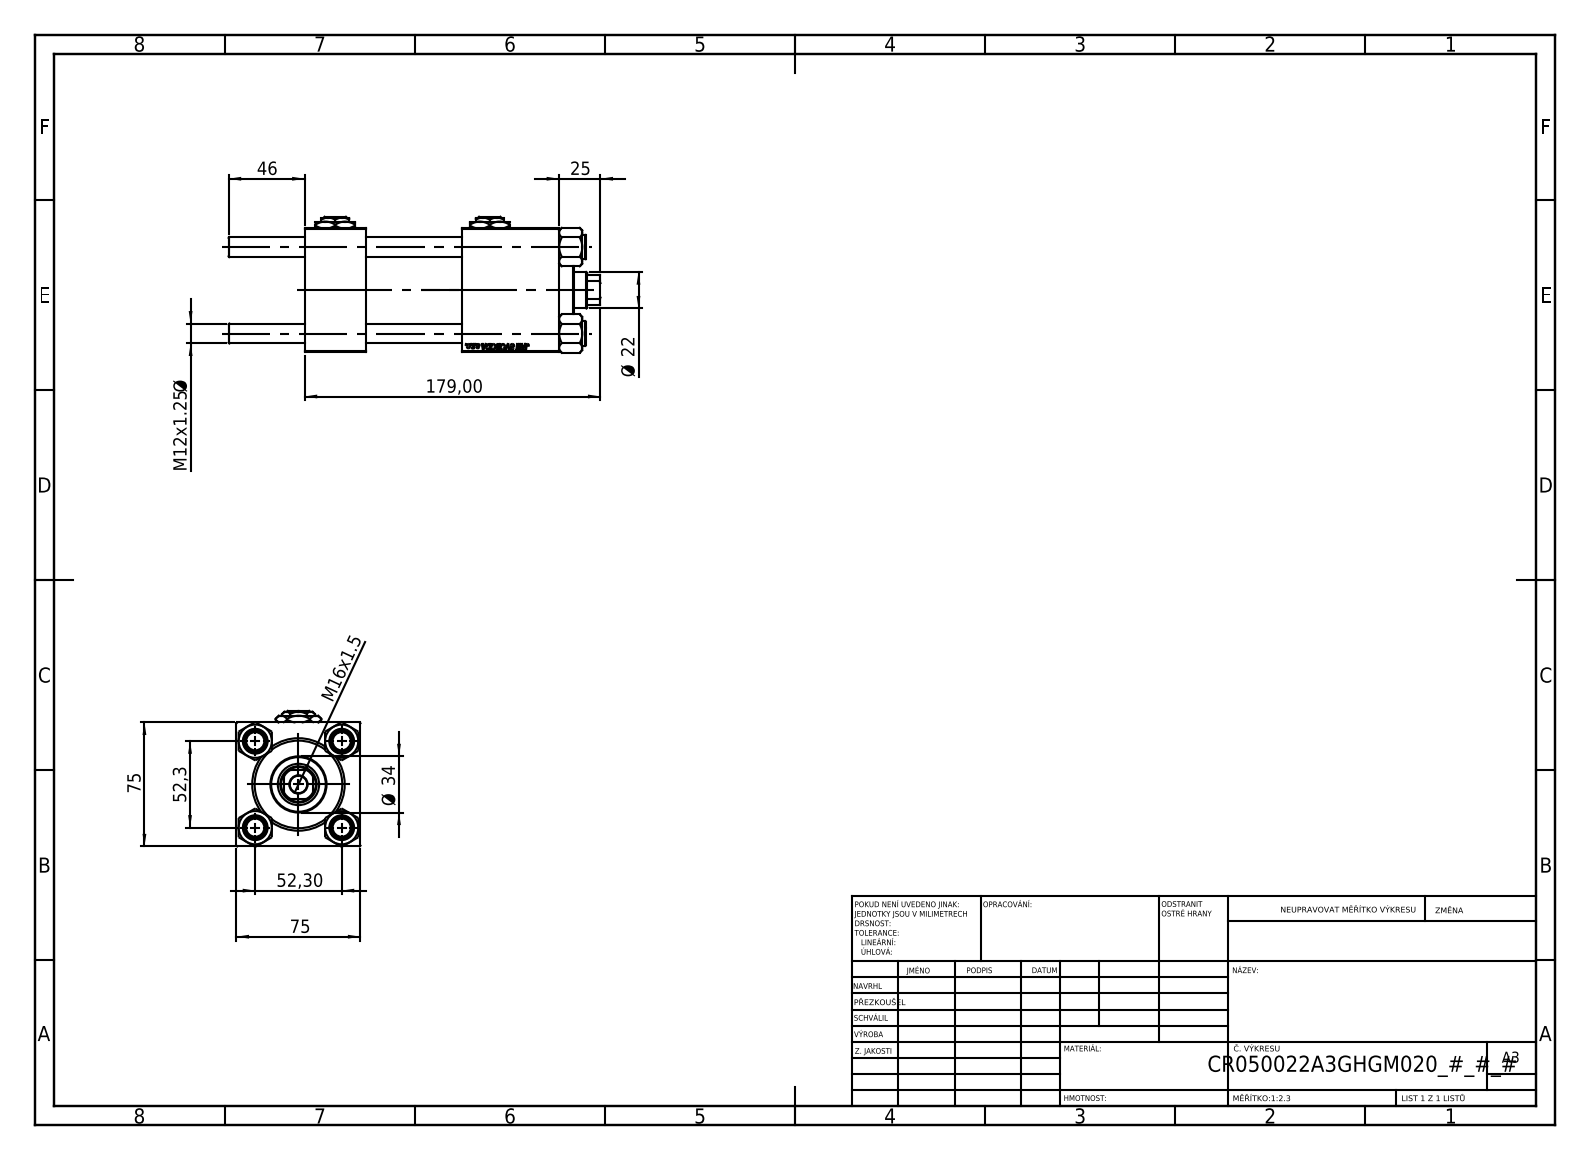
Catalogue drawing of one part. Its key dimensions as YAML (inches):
part_name: "Zatka_pro_OIL_PORT; V215CR_VCP; CR025_012_A_0_G_A_G_M_020_+#_##_TYCINKA; V215CR_BODY_A (+2 more)"
step_written_by: "SolidWorks 2019 (CONFIG_CONTROL_DESIGN)"
units: inches
bodies: {solids: 13, faces: 1233, planar: 567, cylindrical: 88, other: 578}
overall_size: [8.858, 3.239, 2.953]
volume: 41.8
surface_area: 260.7
round_holes:
  - {diameter: 0.472, count: 4}
  - {diameter: 0.276, count: 2}
  - {diameter: 0.825, count: 2}
  - {diameter: 1.181, count: 2}
  - {diameter: 0.413, count: 1}
  - {diameter: 0.866, count: 1}
  - {diameter: 0.984, count: 1}
  - {diameter: 1.614, count: 1}
  - {diameter: 1.969, count: 1}
  - {diameter: 2.087, count: 1}
round_bosses_or_shafts:
  - {diameter: 0.591, count: 4}
  - {diameter: 2.205, count: 1}
  - {diameter: 1.339, count: 1}
partial_cylinders:
  - {radius: 0.413, count: 1}
face_to_face_distances: [2.953, 1.457, 6.063, 4.606, 3.74, 2.323, 2.283, 4.933, 3.476, 1.193]
hole_center_spacings: [1.456, 2.059, 2.912, 3.681]
